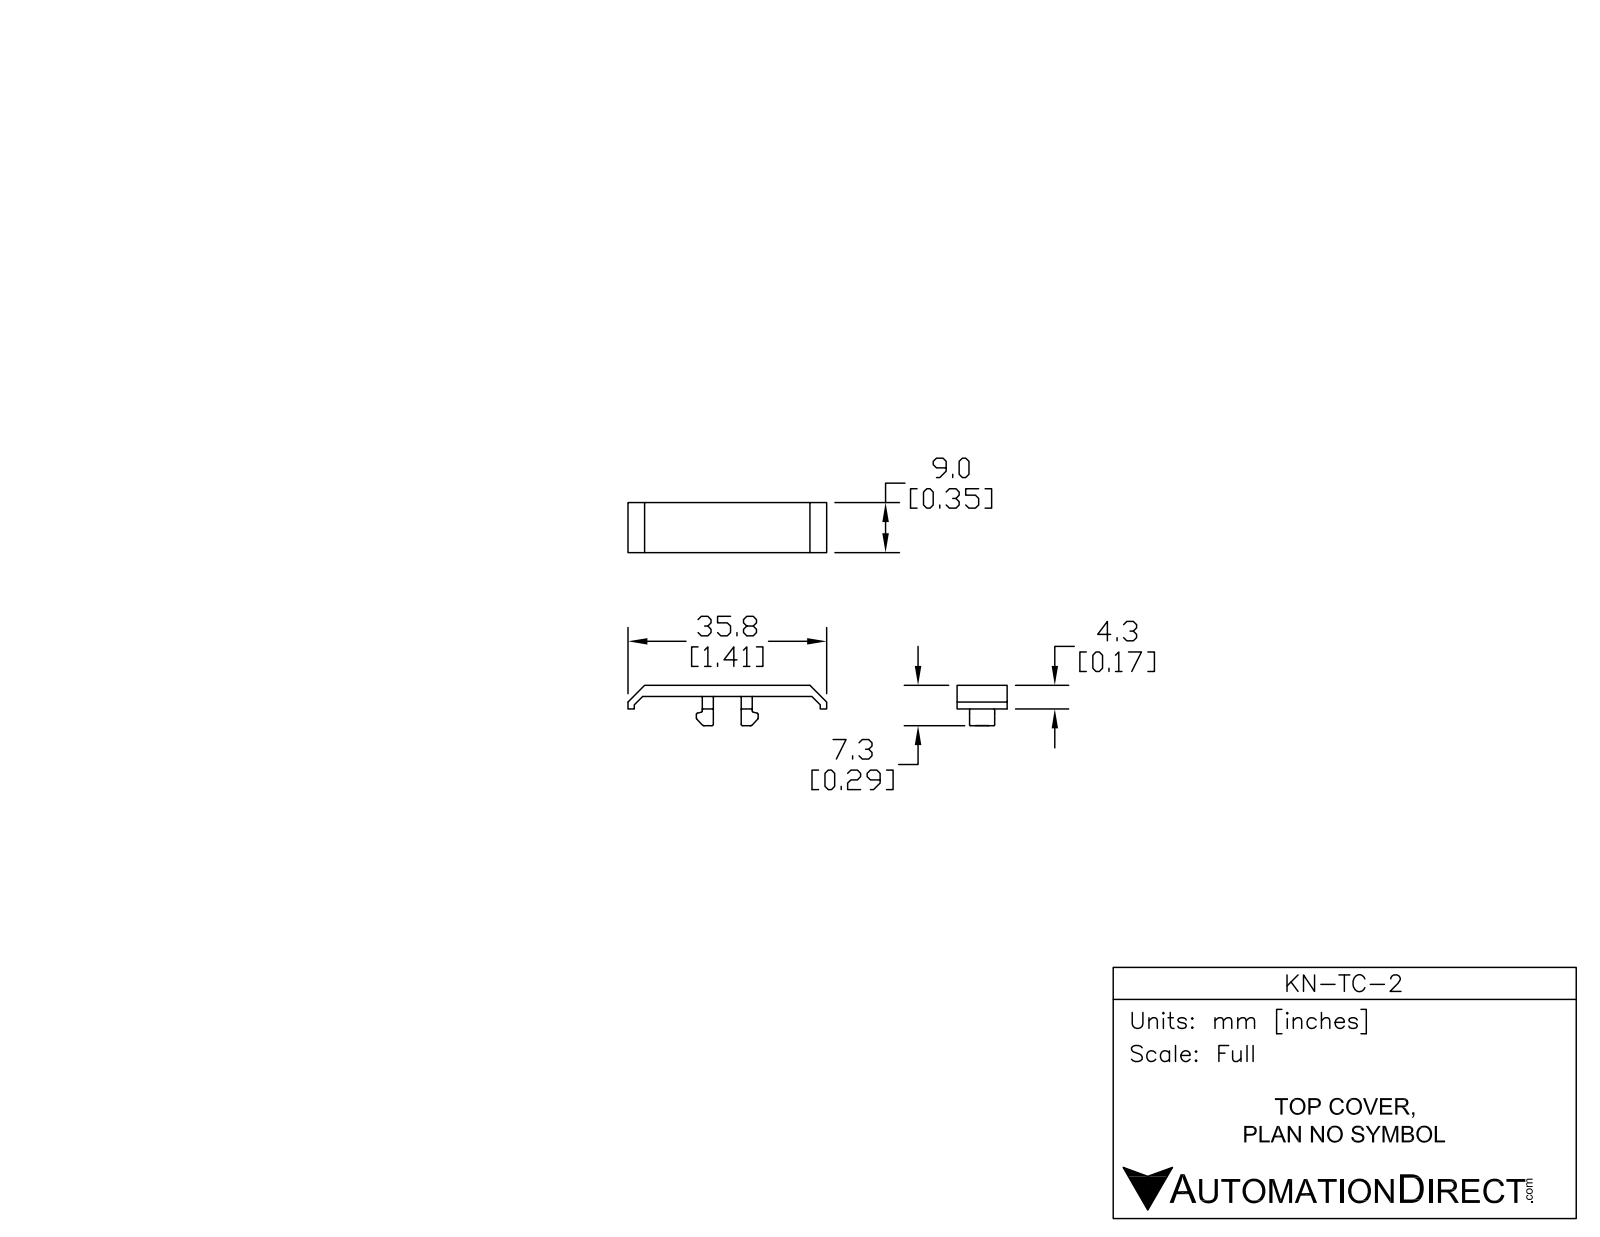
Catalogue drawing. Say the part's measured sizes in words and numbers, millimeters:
The part is named "KN-TC-2". Its 3-D file was written by "SolidWorks 2014 (AUTOMOTIVE_DESIGN)". It is 1 solid with 154 faces: 42 planar, 68 cylindrical and 44 other. Overall it measures 35.75 by 9 by 7.25 millimeters. Its volume is 719 cubic millimeters and its surface area 997 square millimeters. Partial cylindrical surfaces (rounded edges, fillets, slot ends): 44 of radius 0.12, 8 of radius 0.25, 2 of radius 0.3, 2 of radius 0.5. The main face-to-face distances are 2, 9, 1.17, 2.25, 2.24, 6.75, 4.24, 5, 3.38, 5.62.
